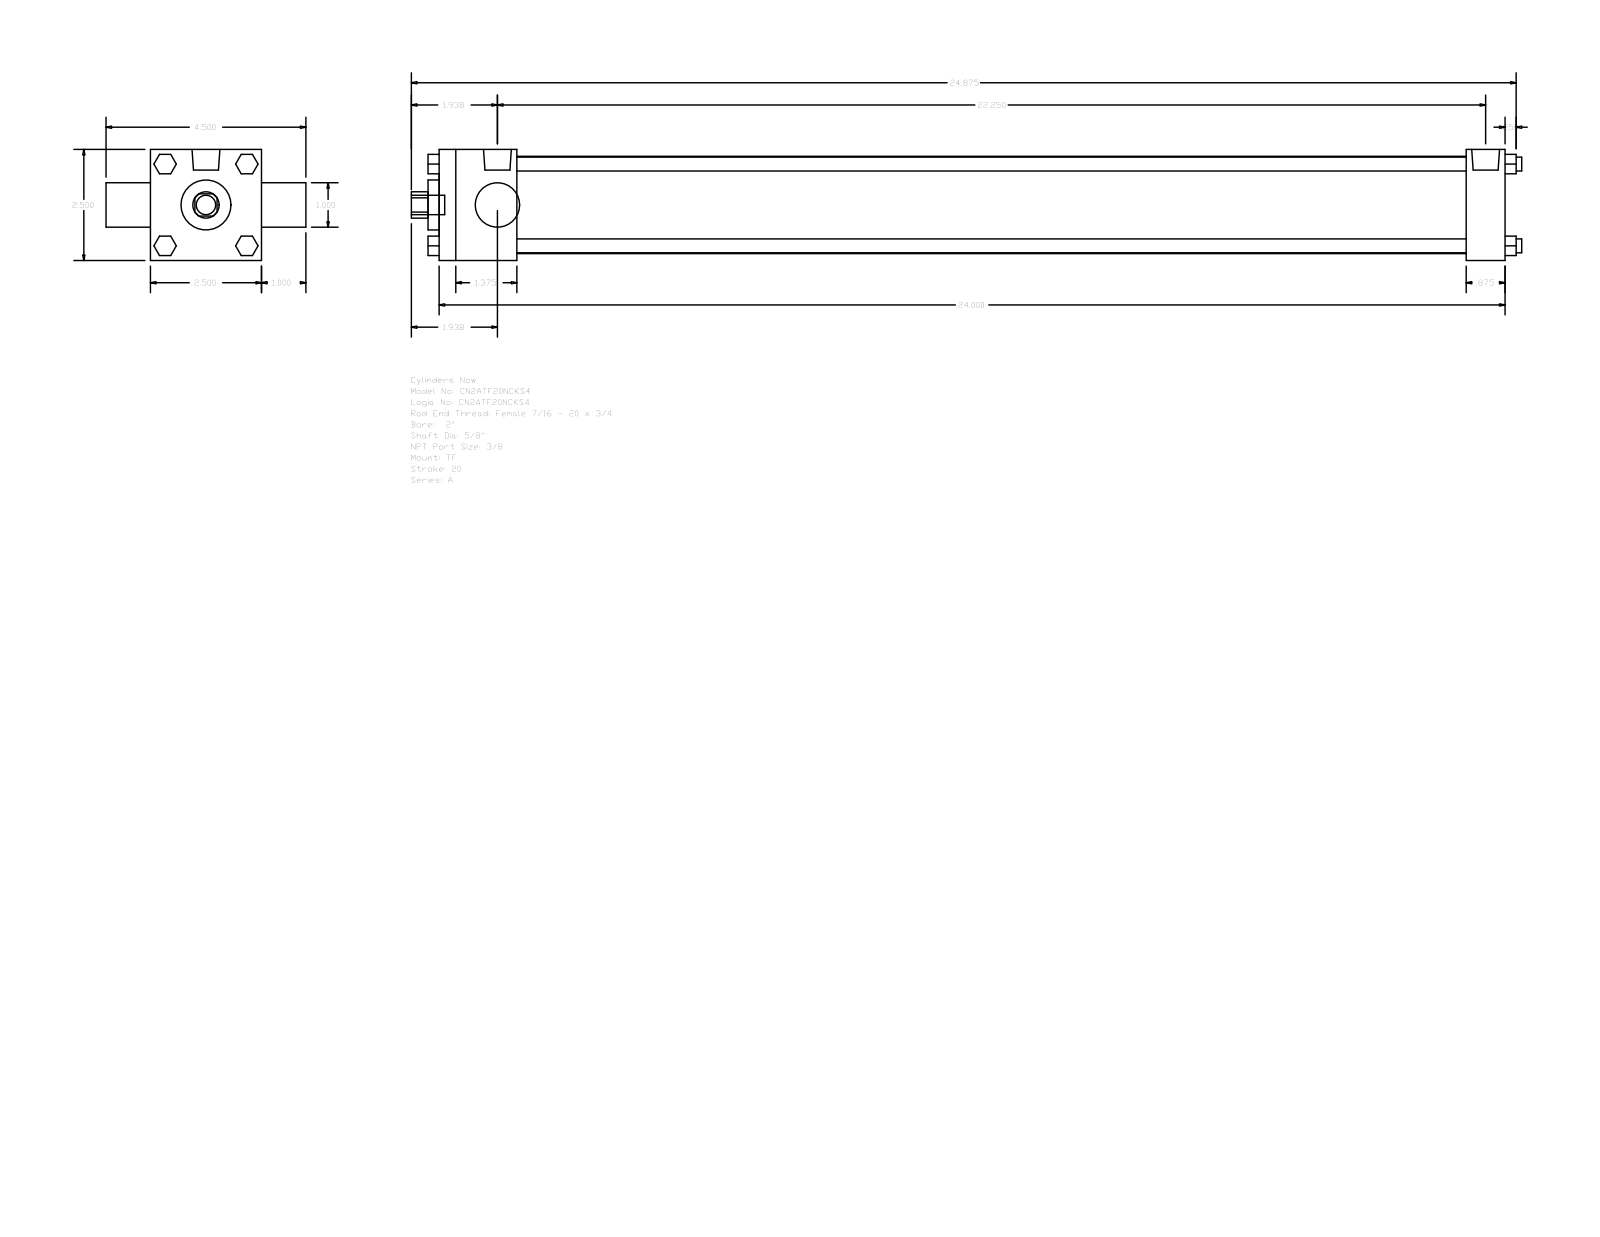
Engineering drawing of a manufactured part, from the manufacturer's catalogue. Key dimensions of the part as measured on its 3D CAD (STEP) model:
Part name (STEP PRODUCT): A_TF__0200_0.625
STEP written by: GSSL Pune (CONFIG_CONTROL_DESIGN)
Units: millimetres
Bodies: 0 solids, 120 faces (92 planar, 28 cylindrical, 0 other)
Overall size (bounding box): 635 × 114.3 × 63.5
Round holes (diameter × count): ⌀15.88 ×1, ⌀25.4 ×1, ⌀28.57 ×1, ⌀55.63 ×1
Round bosses / shafts (diameter × count): ⌀7.94 ×4, ⌀5.56 ×3, ⌀15.93 ×2, ⌀11.11 ×1
Partial cylindrical surfaces — rounded edges, fillets, slot ends (radius × count): R7.54 ×1
Main face-to-face distances: 63.5, 609.6, 44.45, 587.37, 542.92, 565.15, 22.23, 25.4, 88.9, 615.95
